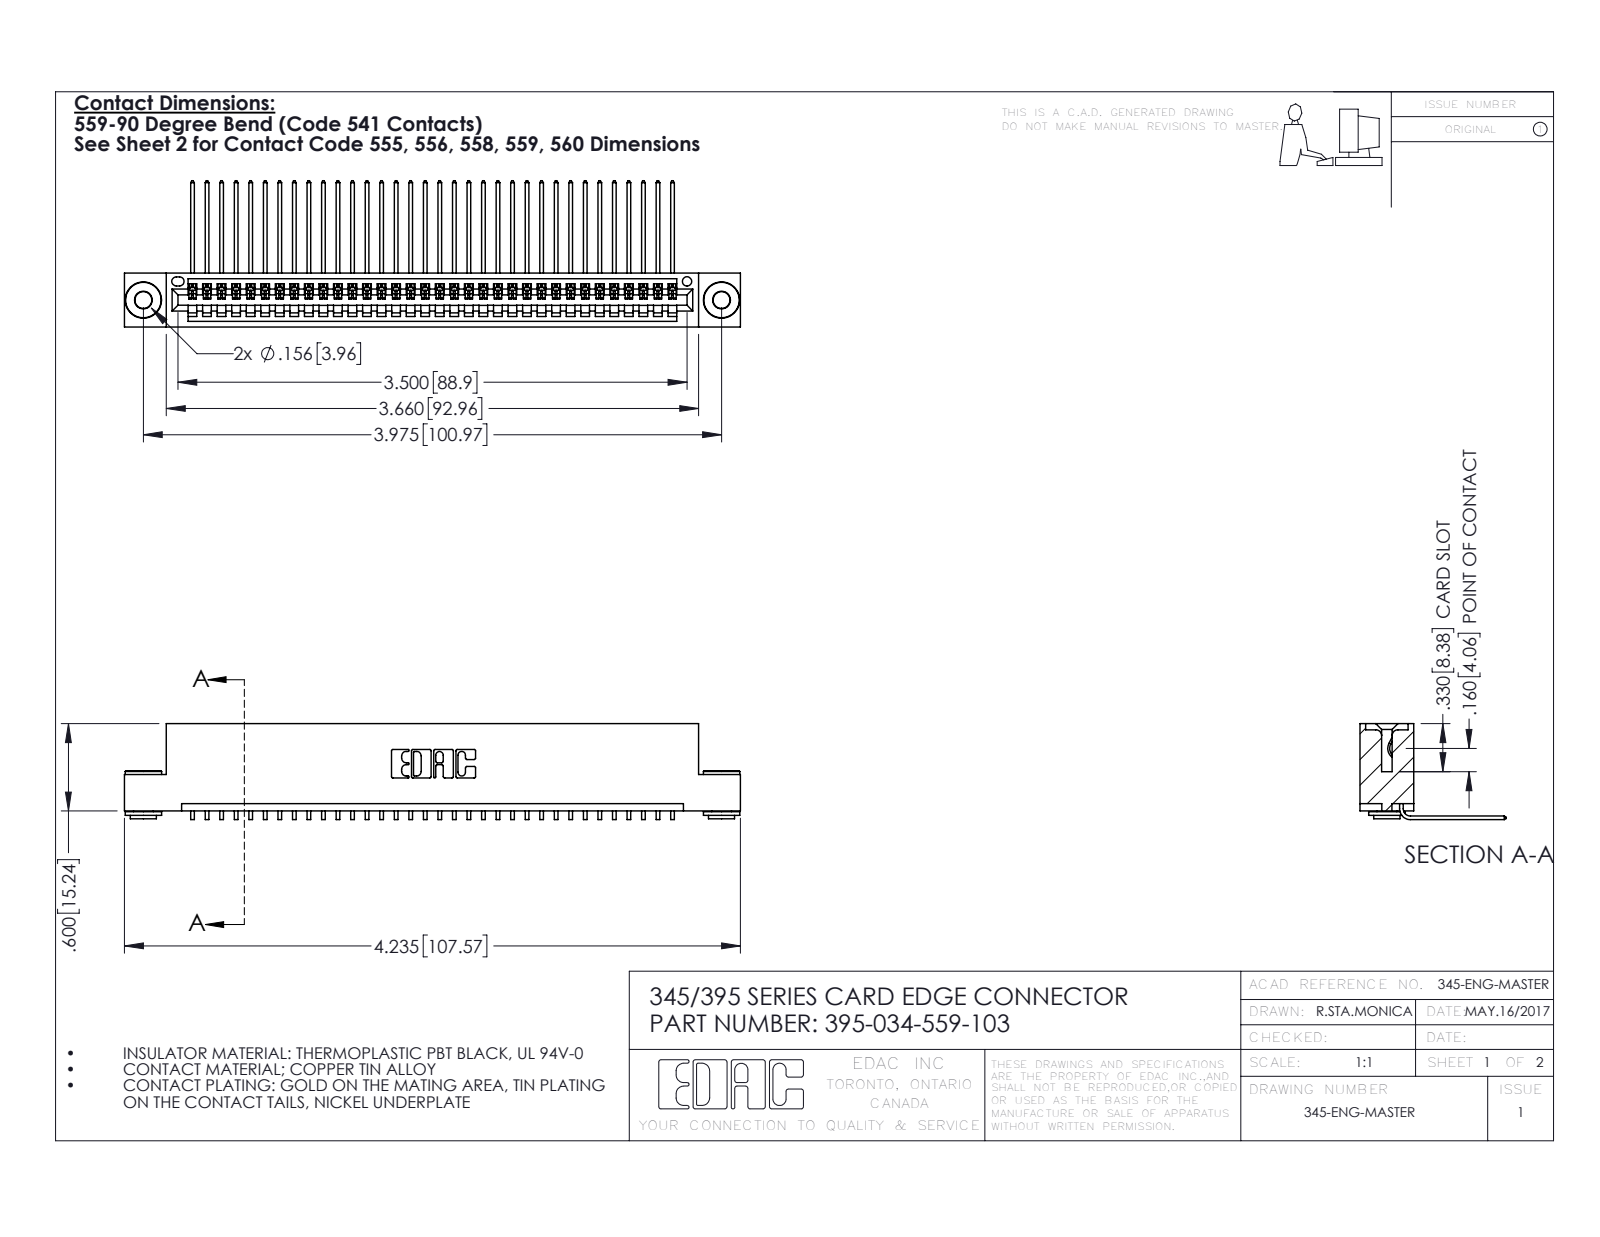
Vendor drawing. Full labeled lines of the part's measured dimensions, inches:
Part name (STEP PRODUCT): 395-034-559-103; 345 Part_Flush Mounting Lugs - 0.156 Dia-TH; 345-292-001_558 559 Tail - 1; 345-250-002_345-250-002-102
STEP written by: SolidWorks 2016 (CONFIG_CONTROL_DESIGN)
Units: inches
Bodies: 37 solids, 2204 faces (1518 planar, 678 cylindrical, 8 other)
Overall size (bounding box): 4.235 × 1.005 × 0.659
Volume: 0.628 in³ · Surface area: 22.38 in²
Round holes (diameter × count): ⌀0.116 ×2, ⌀0.156 ×2, ⌀0.064 ×1
Round bosses / shafts (diameter × count): ⌀0.25 ×2, ⌀0.18 ×2, ⌀0.136 ×2
Partial cylindrical surfaces — rounded edges, fillets, slot ends (radius × count): R0.006 ×68, R0.01 ×22, R0.007 ×6, R0.031 ×6, R0.026 ×3, R0.031 ×2, R0.04 ×2, R0.014 ×1
Main face-to-face distances: 0.072, 0.298, 0.37, 0.2, 0.025, 0.098, 0.272, 0.225, 0.149, 0.072
Hole centre spacings: 0.27, 3.74, 3.975
